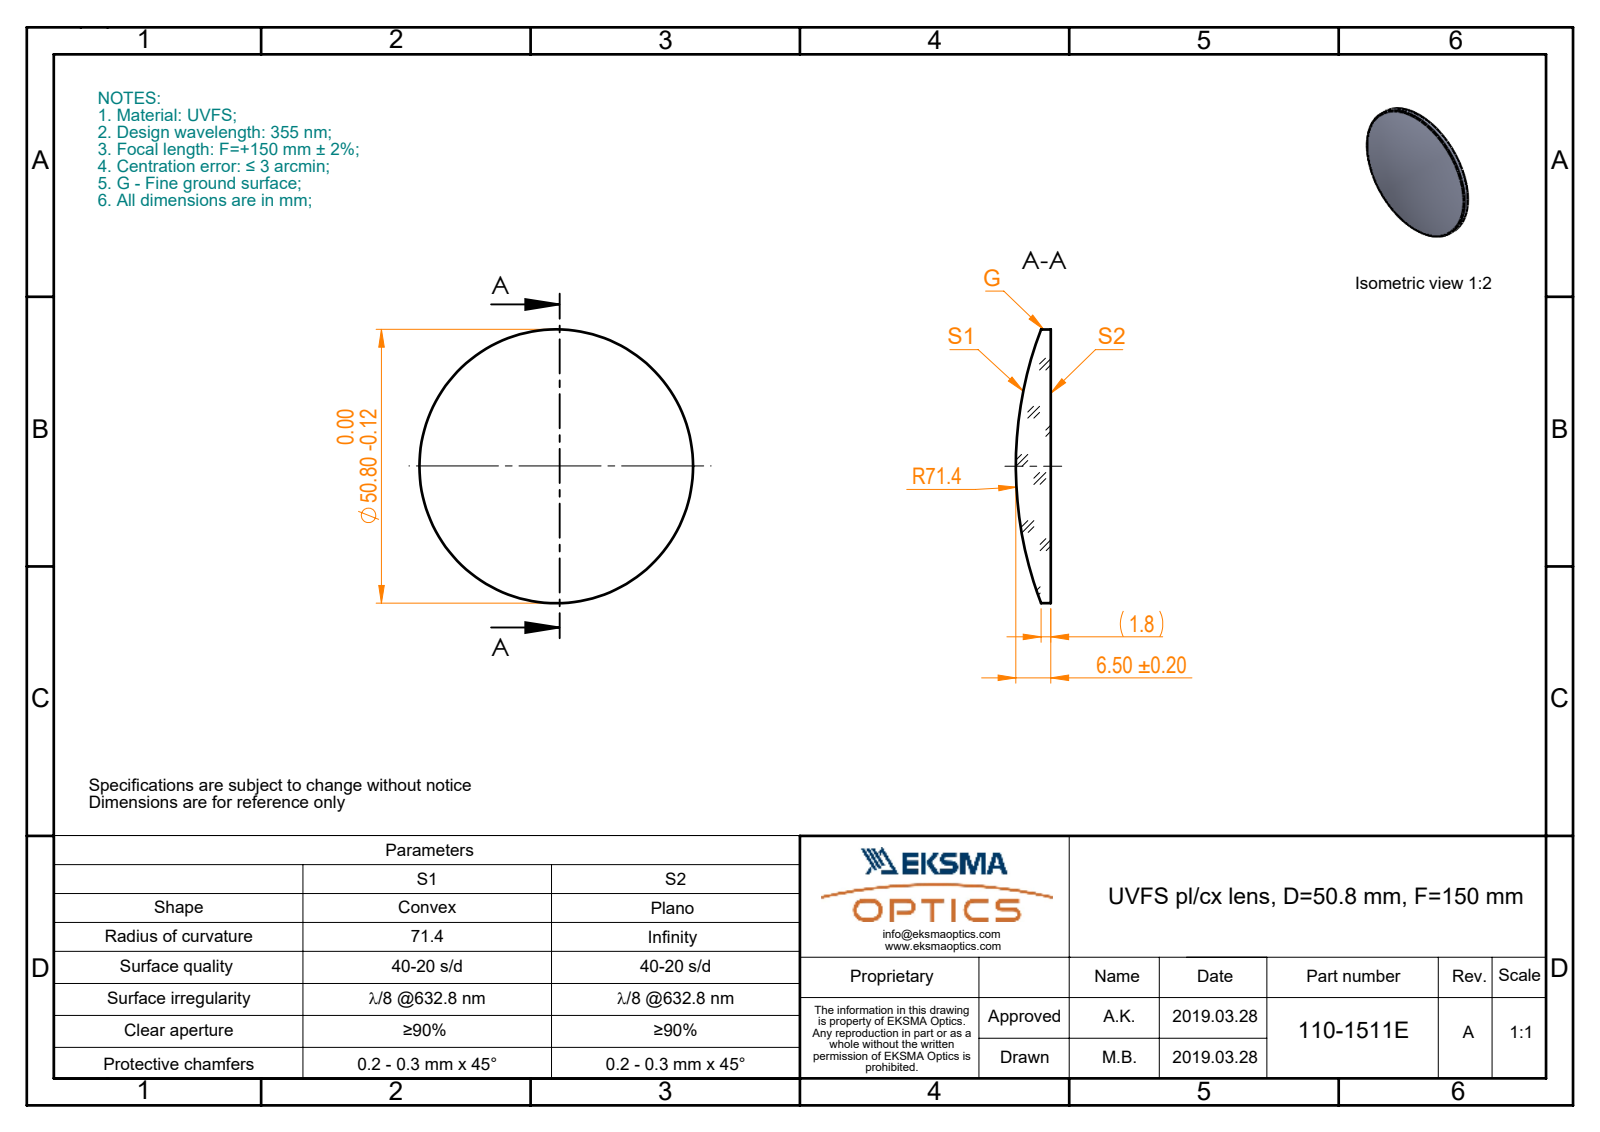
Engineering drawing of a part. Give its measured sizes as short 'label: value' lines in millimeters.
name: 110-1511E UVFS pl-cx 50.8 F150
written by: SolidWorks 2017 (CONFIG_CONTROL_DESIGN)
unit: mm
bodies: 1 solid, 5 faces (1 planar, 2 cylindrical, 2 other)
size: 50.8 × 50.8 × 6.5
volume: 8 495 mm³; area: 4 414 mm²
bosses: 1× ⌀50.8
